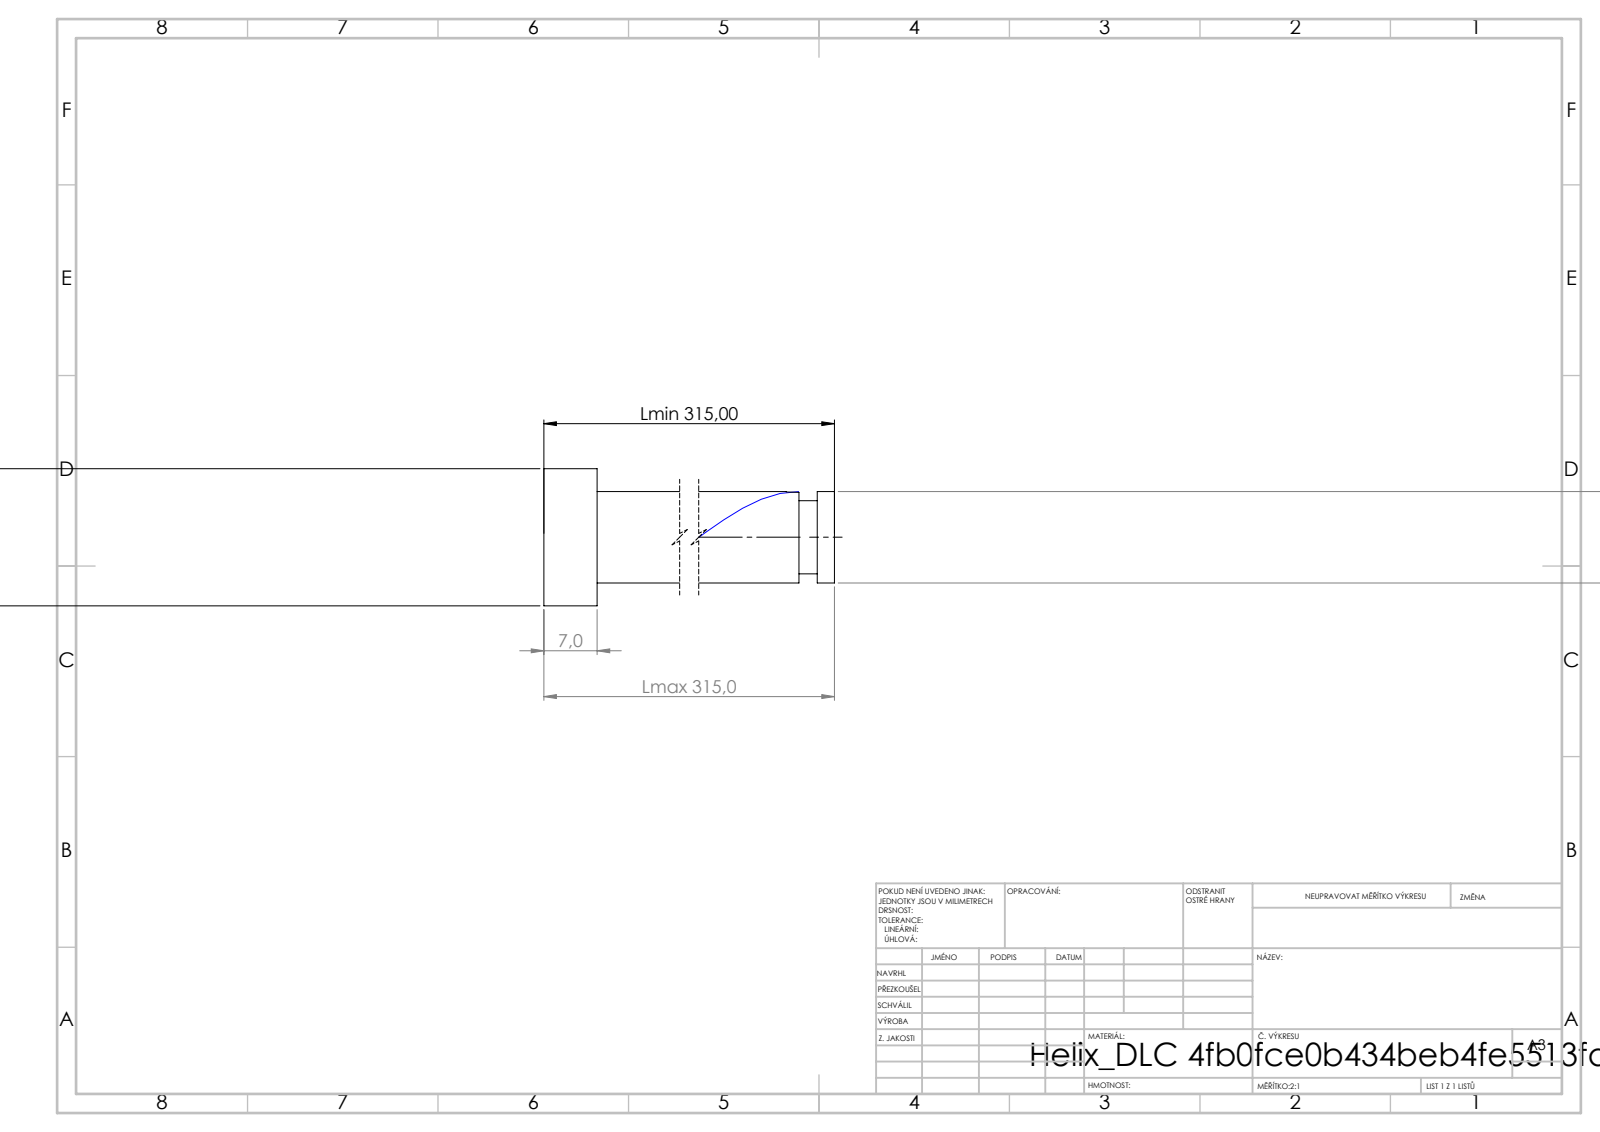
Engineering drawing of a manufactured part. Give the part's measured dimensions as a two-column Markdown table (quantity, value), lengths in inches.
| quantity | value |
| --- | --- |
| STEP written by | SolidWorks 2019 (CONFIG_CONTROL_DESIGN) |
| units | inches |
| bodies | 1 solid, 21 faces (6 planar, 14 cylindrical, 1 other) |
| overall size | 12.402 × 0.709 × 0.709 |
| volume | 2.208 in³ |
| surface area | 19.87 in² |
| round bosses / shafts (diameter × count) | 0.709 × 1, 0.472 × 1, 0.378 × 1 |
| main face-to-face distances | 0.276, 12.402, 12.126, 12.312, 12.037, 0.089, 12.218, 11.942, 0.094, 0.184 |
